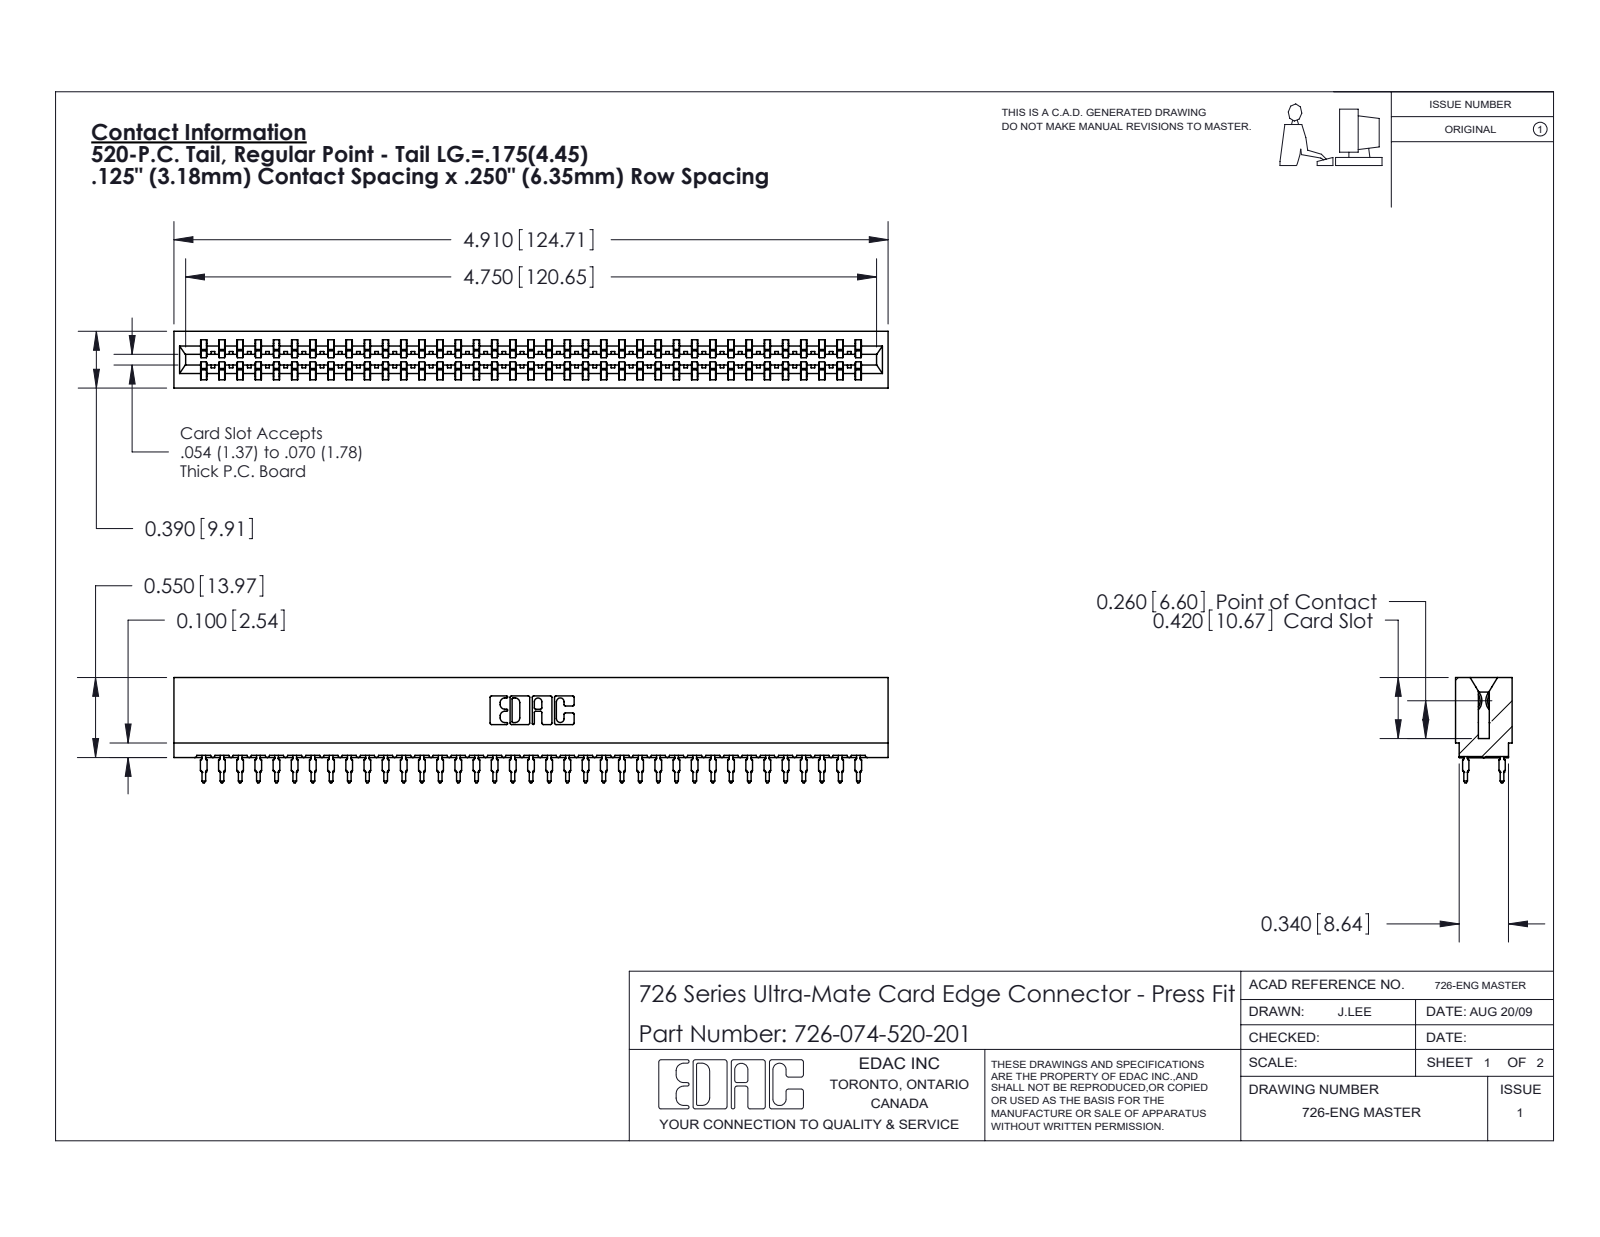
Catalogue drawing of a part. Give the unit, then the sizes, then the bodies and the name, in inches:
Units: inches
Overall size (bounding box): 4.91 × 0.724 × 0.39
Partial cylindrical surfaces — rounded edges, fillets, slot ends (radius × count): R0.021 ×148, R0.015 ×38, R0.01 ×22, R0.005 ×8, R0.011 ×8, R0.007 ×6, R0.031 ×6, R0.026 ×3
Main face-to-face distances: 0.057, 0.333, 0.39, 0.25, 0.025, 0.307, 0.275, 0.083, 0.5, 0.365
Volume: 0.698 in³ · Surface area: 28.92 in²
Bodies: 75 solids, 6720 faces (3459 planar, 1337 cylindrical, 1924 other)
Part name (STEP PRODUCT): 726-074-520-201; 726 Part_.515 Slot Depth - 01; 746-292-001_520
STEP written by: SolidWorks 2020 (CONFIG_CONTROL_DESIGN)
